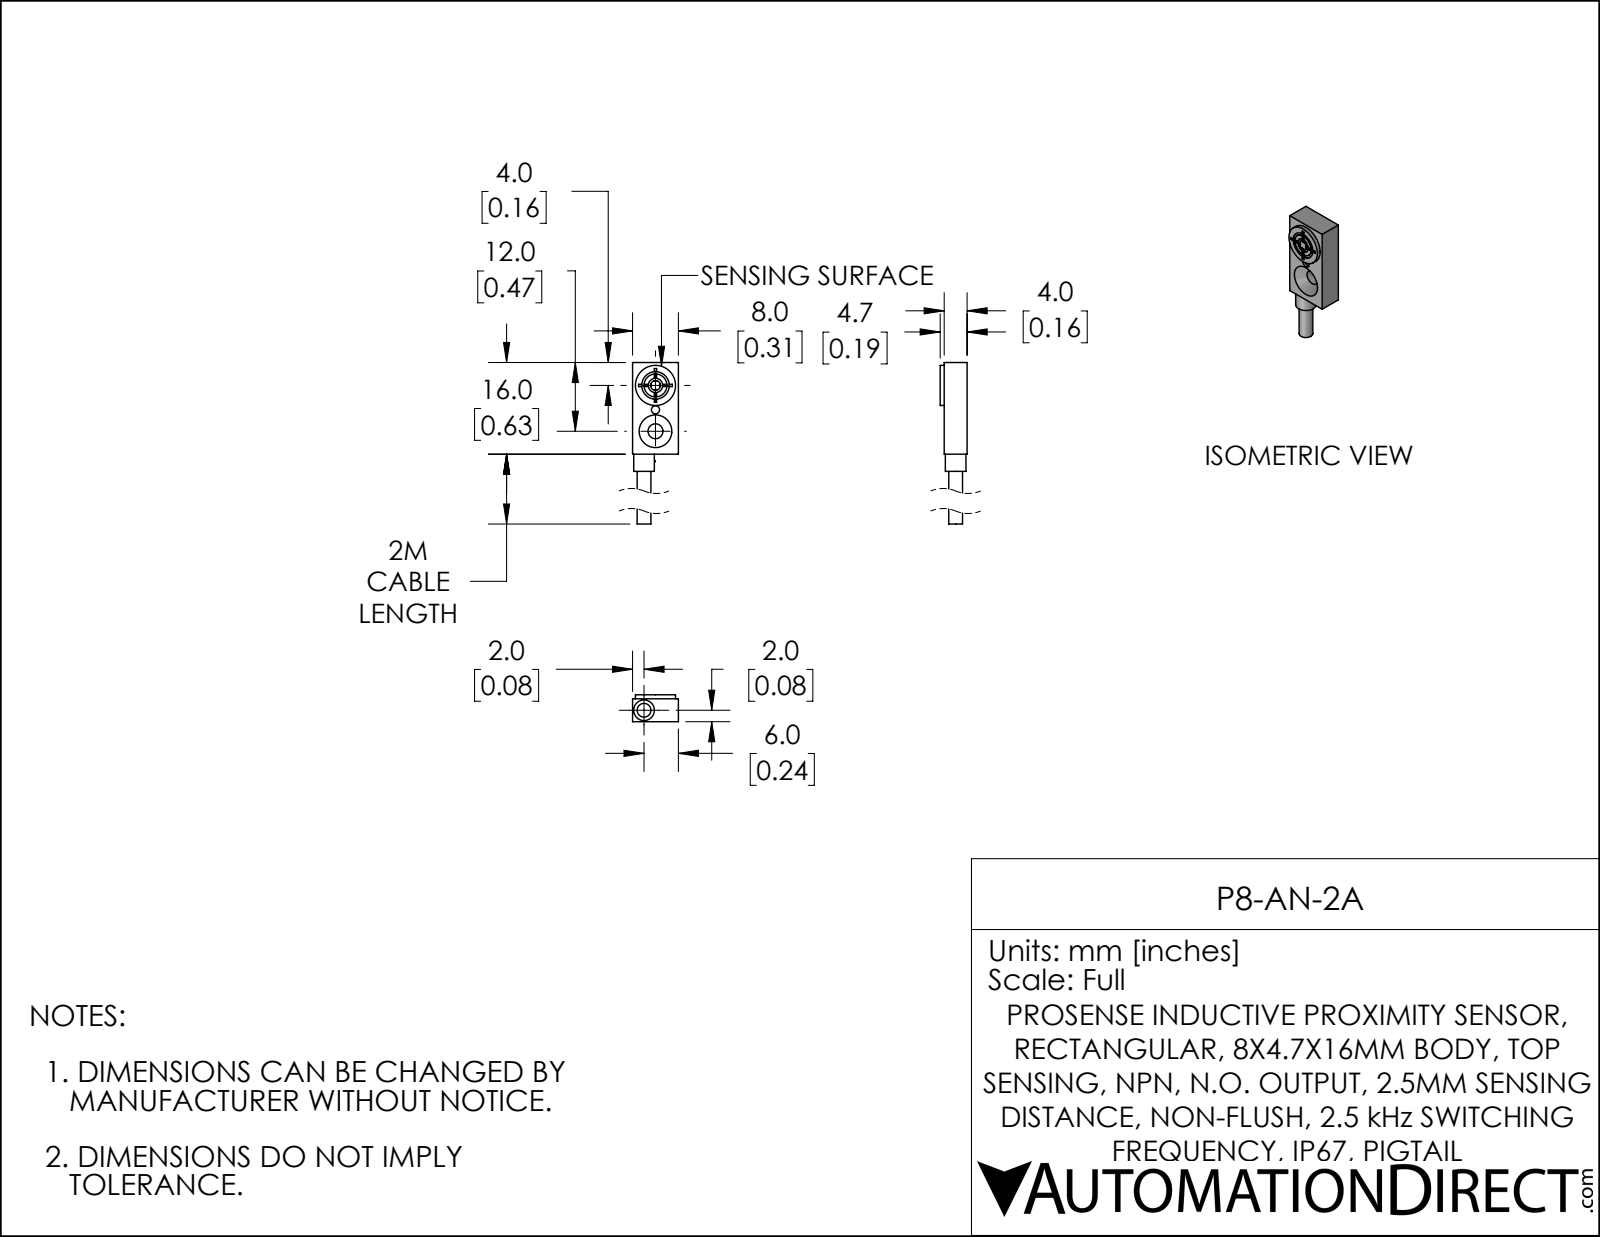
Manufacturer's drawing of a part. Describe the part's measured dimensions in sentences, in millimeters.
The part is named "P8-AN-2A". Its 3-D file was written by "SolidWorks 2019 (AUTOMOTIVE_DESIGN)". It is 1 solid with 70 faces: 48 planar, 21 cylindrical and 1 other. Overall it measures 25.2 by 8 by 4.7 millimeters. Its volume is 560 cubic millimeters and its surface area 566 square millimeters. Round holes: 1 of diameter 1.4, 1 of diameter 2.5, 1 of diameter 2.6, 1 of diameter 4.8. Round bosses or shafts: 1 of diameter 7, 1 of diameter 4, 1 of diameter 3.6, 1 of diameter 2.4. Partial cylindrical surfaces (rounded edges, fillets, slot ends): 1 of radius 0.8. The main face-to-face distances are 8, 4, 4.7, 0.7, 16, 4.6, 0.7, 19, 3, 25.2. The hole center spacings are 3.8, 4.2, 8.
